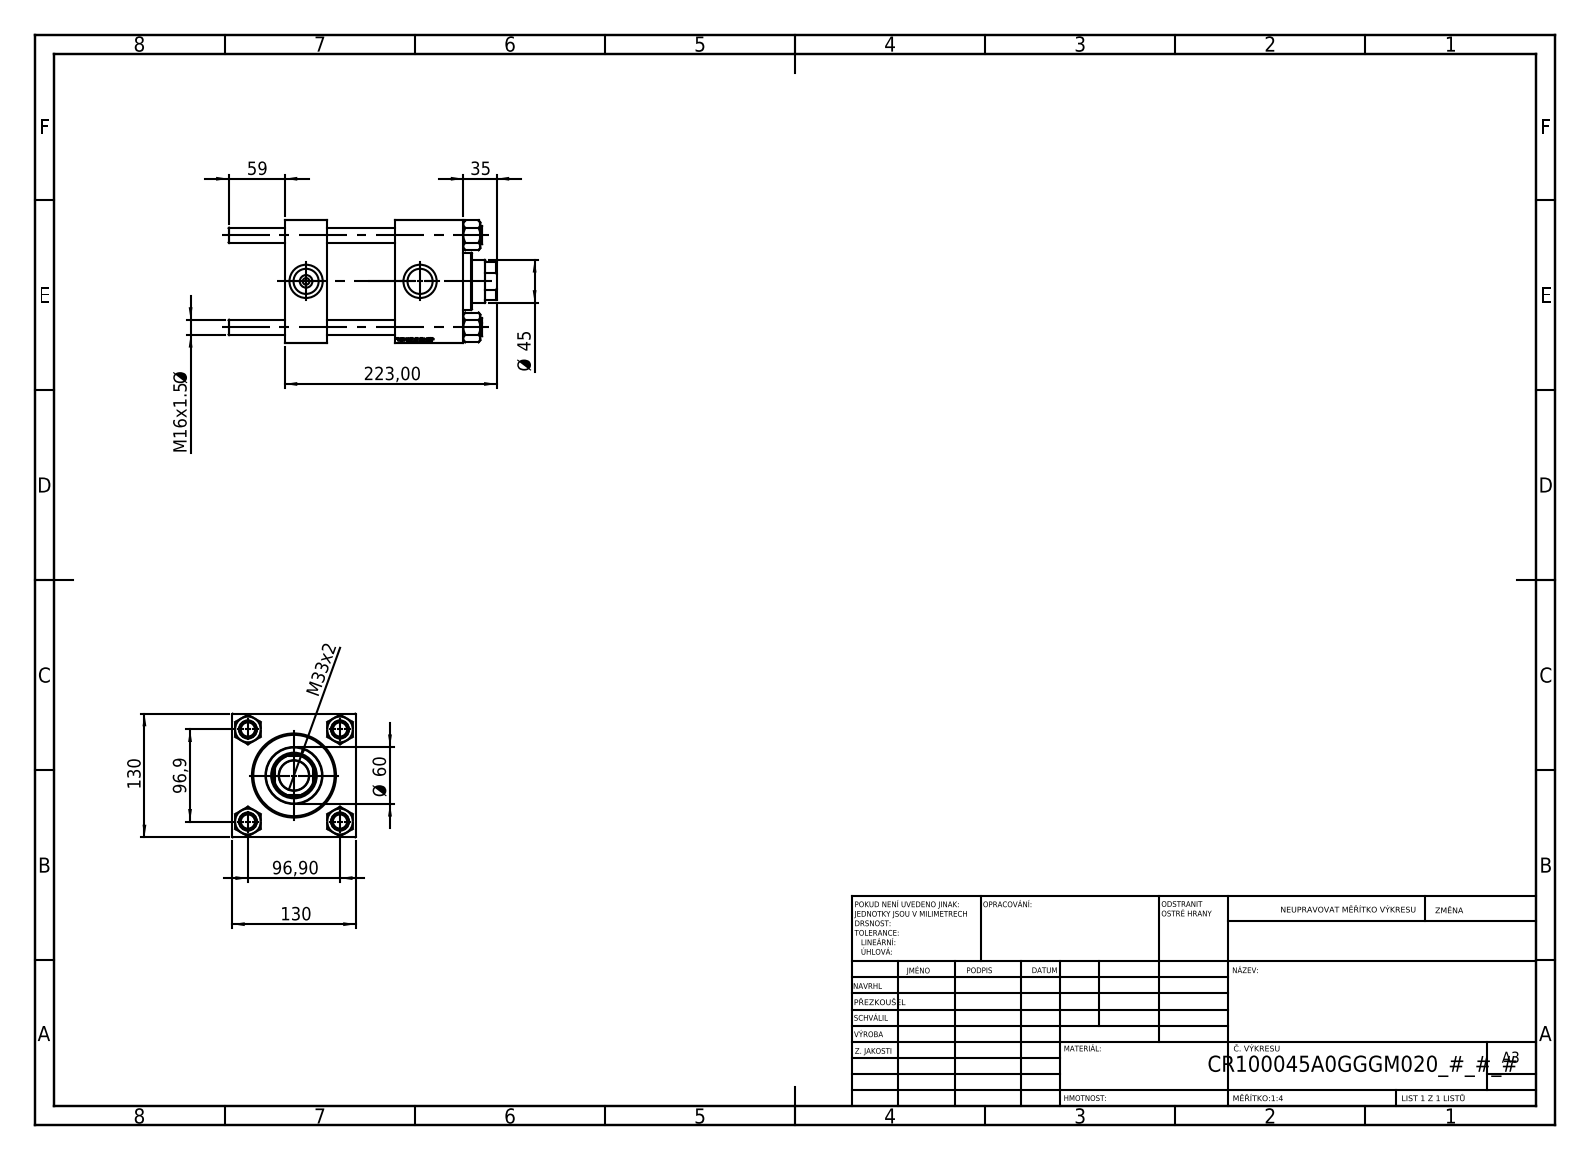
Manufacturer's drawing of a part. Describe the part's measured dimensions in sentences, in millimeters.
The part is named "CR025_012_A_0_G_A_G_M_020_+#_##_TYCINKA; V215CR_VCP; V215_VC_A; NUT_M5 (+1 more)". Its 3-D file was written by "SolidWorks 2019 (CONFIG_CONTROL_DESIGN)". It is 11 solids with 1182 faces: 567 planar, 79 cylindrical and 536 other. Overall it measures 282 by 130 by 130 millimeters. Its volume is 2 502 000 cubic millimeters and its surface area 354 589 square millimeters. Round holes: 4 of diameter 16, 2 of diameter 7, 2 of diameter 26.44, 2 of diameter 35, 1 of diameter 31.5, 1 of diameter 45, 1 of diameter 48, 1 of diameter 76, 1 of diameter 85.5, 1 of diameter 100. Round bosses or shafts: 4 of diameter 19, 1 of diameter 106, 1 of diameter 60. Partial cylindrical surfaces (rounded edges, fillets, slot ends): 1 of radius 22. The main face-to-face distances are 130, 45, 188, 143, 116, 71, 72, 20, 92, 96. The hole center spacings are 68.52, 96.9, 137.04, 119.94.
